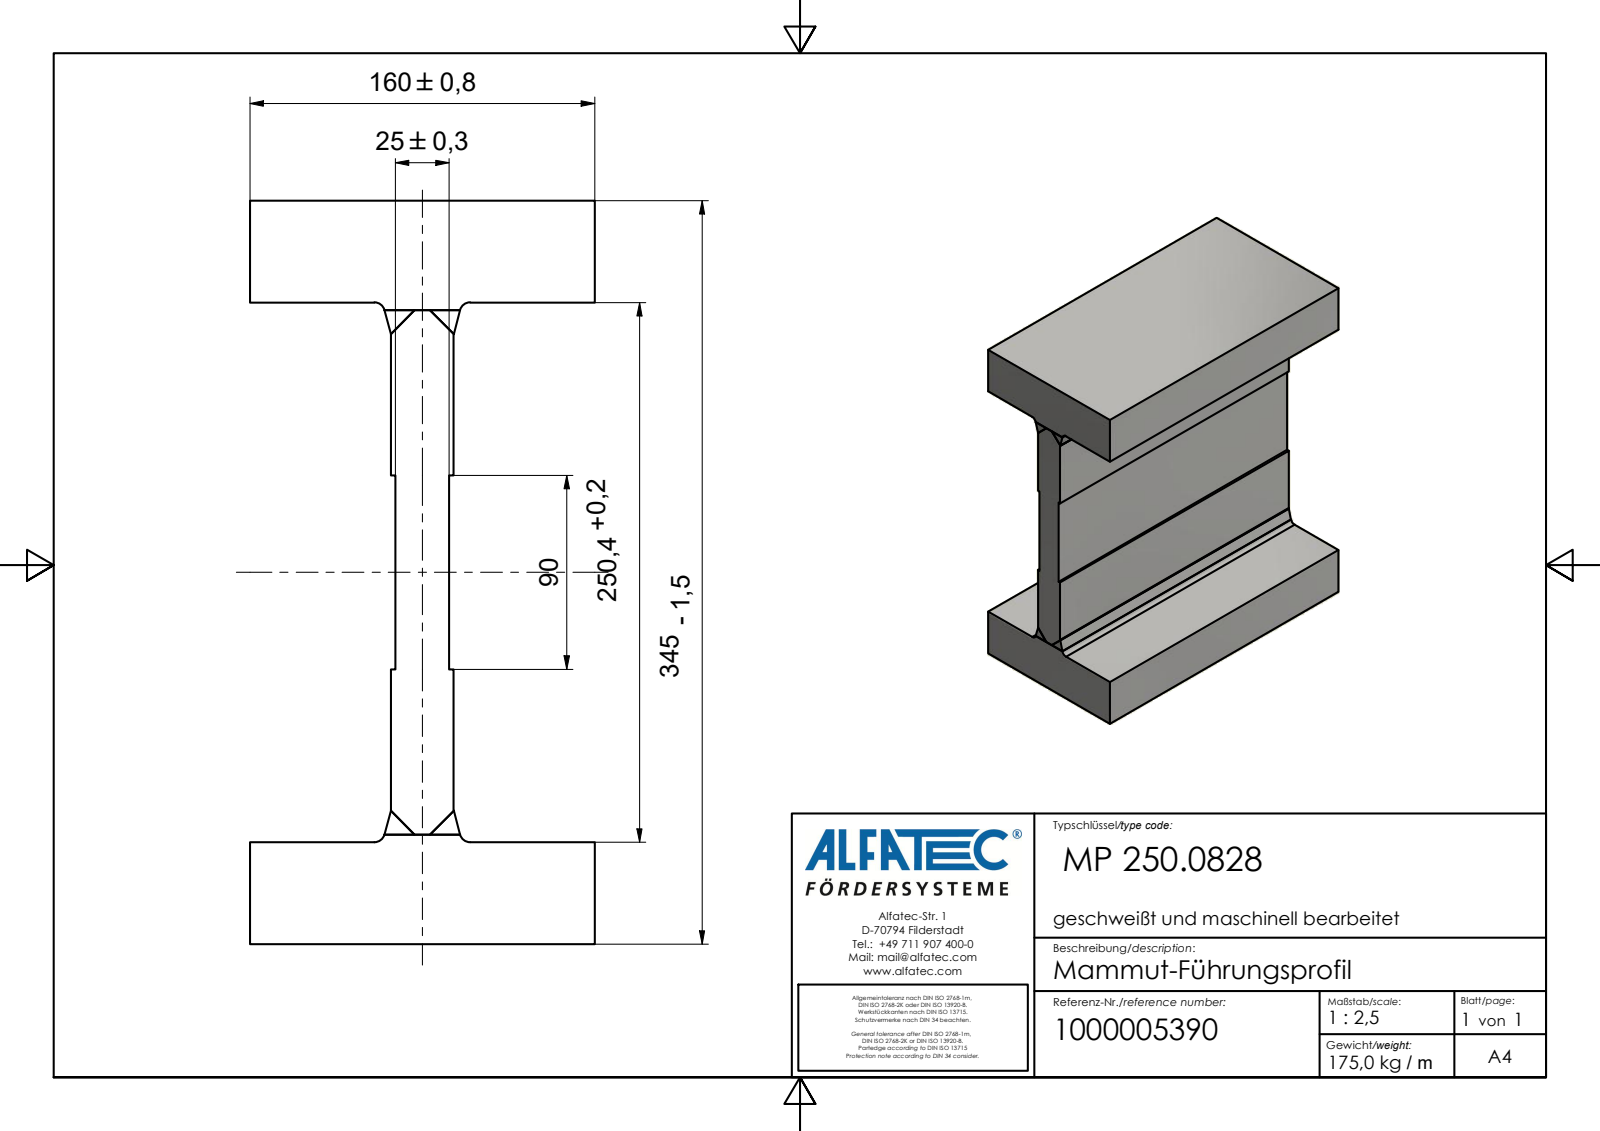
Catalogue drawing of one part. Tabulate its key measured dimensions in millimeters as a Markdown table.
| quantity | value |
| --- | --- |
| part name | ALFATEC_MP 250_0828_Kontur |
| STEP written by | Autodesk Inventor 2020 (AUTOMOTIVE_DESIGN) |
| units | millimeters |
| bodies | 1 solid, 30 faces (26 planar, 4 cylindrical, 0 other) |
| overall size | 345 × 300 × 160 |
| volume | 6 651 000 mm³ |
| surface area | 422 849 mm² |
| partial cylindrical surfaces (radius × count) | 4.8 × 4 |
| main face-to-face distances | 47.3, 297.7, 65.5, 94.5, 67.5, 92.5, 2, 27, 345, 29 |
